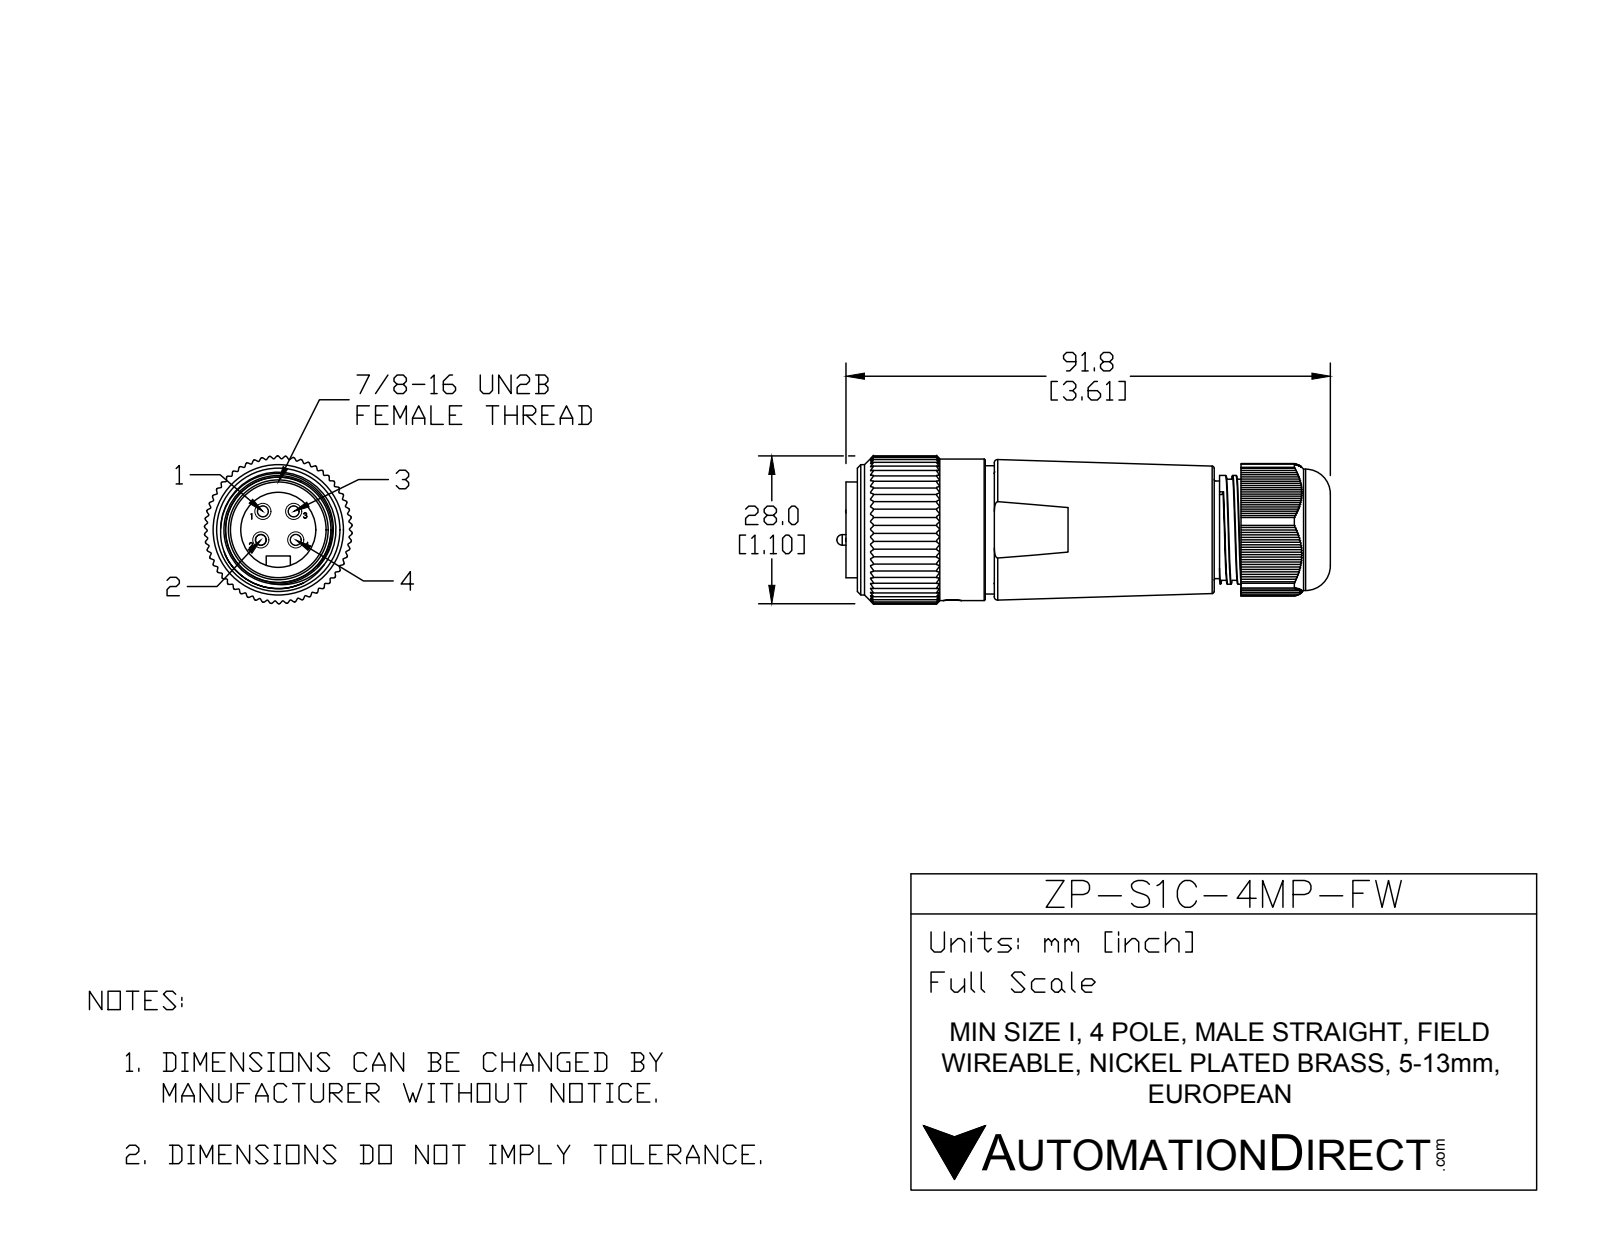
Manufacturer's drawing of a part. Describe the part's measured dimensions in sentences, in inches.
The part is named "ZP-S1C-4MP-FW". Its 3-D file was written by "SolidWorks 2017 (AUTOMOTIVE_DESIGN)". It is 8 solids with 846 faces: 454 planar, 321 cylindrical and 71 other. Overall it measures 3.676 by 1.102 by 1.102 inches. Its volume is 2.501 cubic inches and its surface area 24.38 square inches. Round holes: 1 of diameter 0.14, 1 of diameter 0.53, 1 of diameter 0.56, 1 of diameter 0.72, 1 of diameter 0.849, 1 of diameter 0.953, 1 of diameter 1. Round bosses or shafts: 4 of diameter 0.124, 4 of diameter 0.079, 1 of diameter 1.055, 1 of diameter 0.957, 1 of diameter 0.905, 1 of diameter 0.875, 1 of diameter 0.811, 1 of diameter 0.714. Partial cylindrical surfaces (rounded edges, fillets, slot ends): 165 of radius 0.01, 1 of radius 0.09, 1 of radius 0.521, 1 of radius 0.551. The main face-to-face distances are 2.652, 0.042, 0.014, 0.028, 0.346, 2.306, 0.056, 0.083, 0.07, 0.014.
